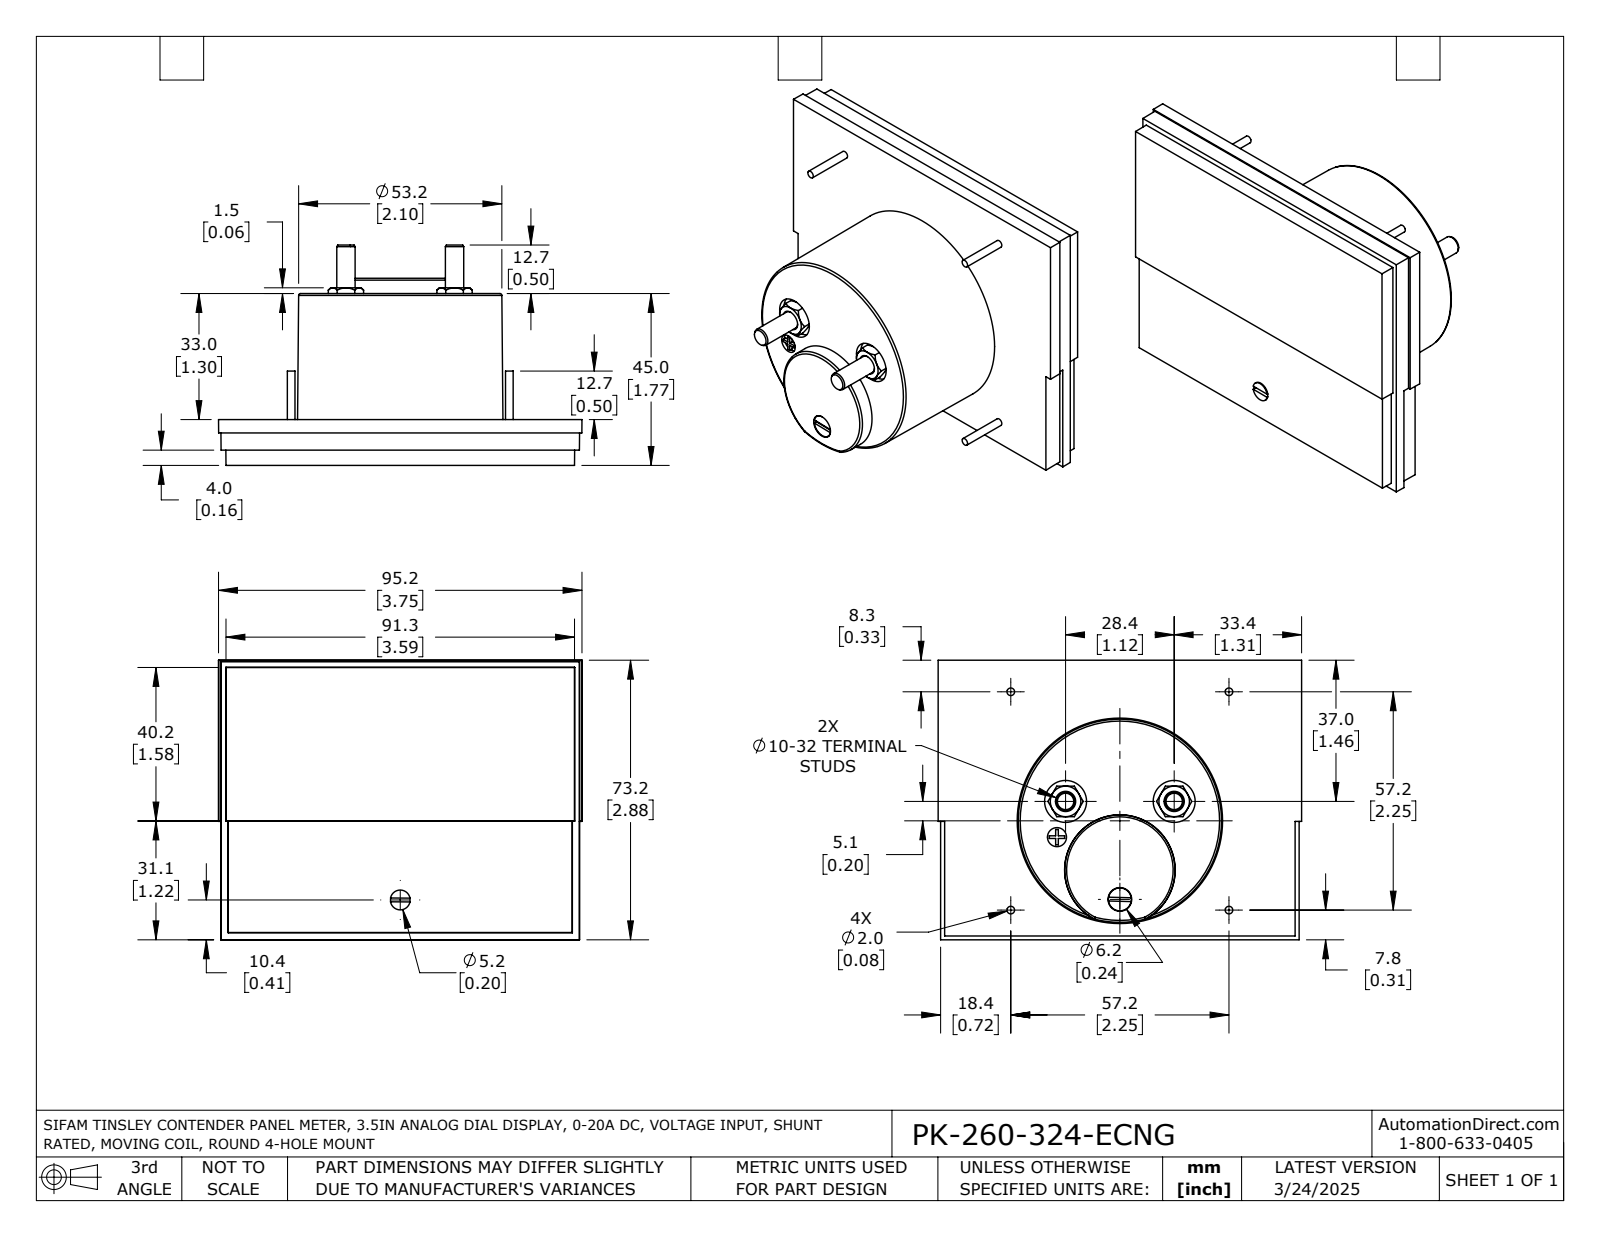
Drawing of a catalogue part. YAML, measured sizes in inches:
part_name: "PK-260-324-ECNG"
step_written_by: "SolidWorks 2021 (AUTOMOTIVE_DESIGN)"
units: inches
bodies: {solids: 1, faces: 163, planar: 76, cylindrical: 31, other: 56}
overall_size: [3.748, 2.882, 2.272]
volume: 9.446
surface_area: 38.39
round_holes:
  - {diameter: 0.433, count: 2}
  - {diameter: 0.197, count: 1}
  - {diameter: 0.244, count: 1}
round_bosses_or_shafts:
  - {diameter: 0.079, count: 4}
  - {diameter: 0.189, count: 2}
  - {diameter: 0.236, count: 1}
  - {diameter: 0.205, count: 1}
partial_cylinders:
  - {radius: 0.1, count: 1}
face_to_face_distances: [0.472, 0.03, 0.443, 1.772, 1.299, 1.742, 0.157, 0.073, 0.315, 1.457]
hole_center_spacings: [1.155, 0.379, 0.912, 1.12, 1.263]
